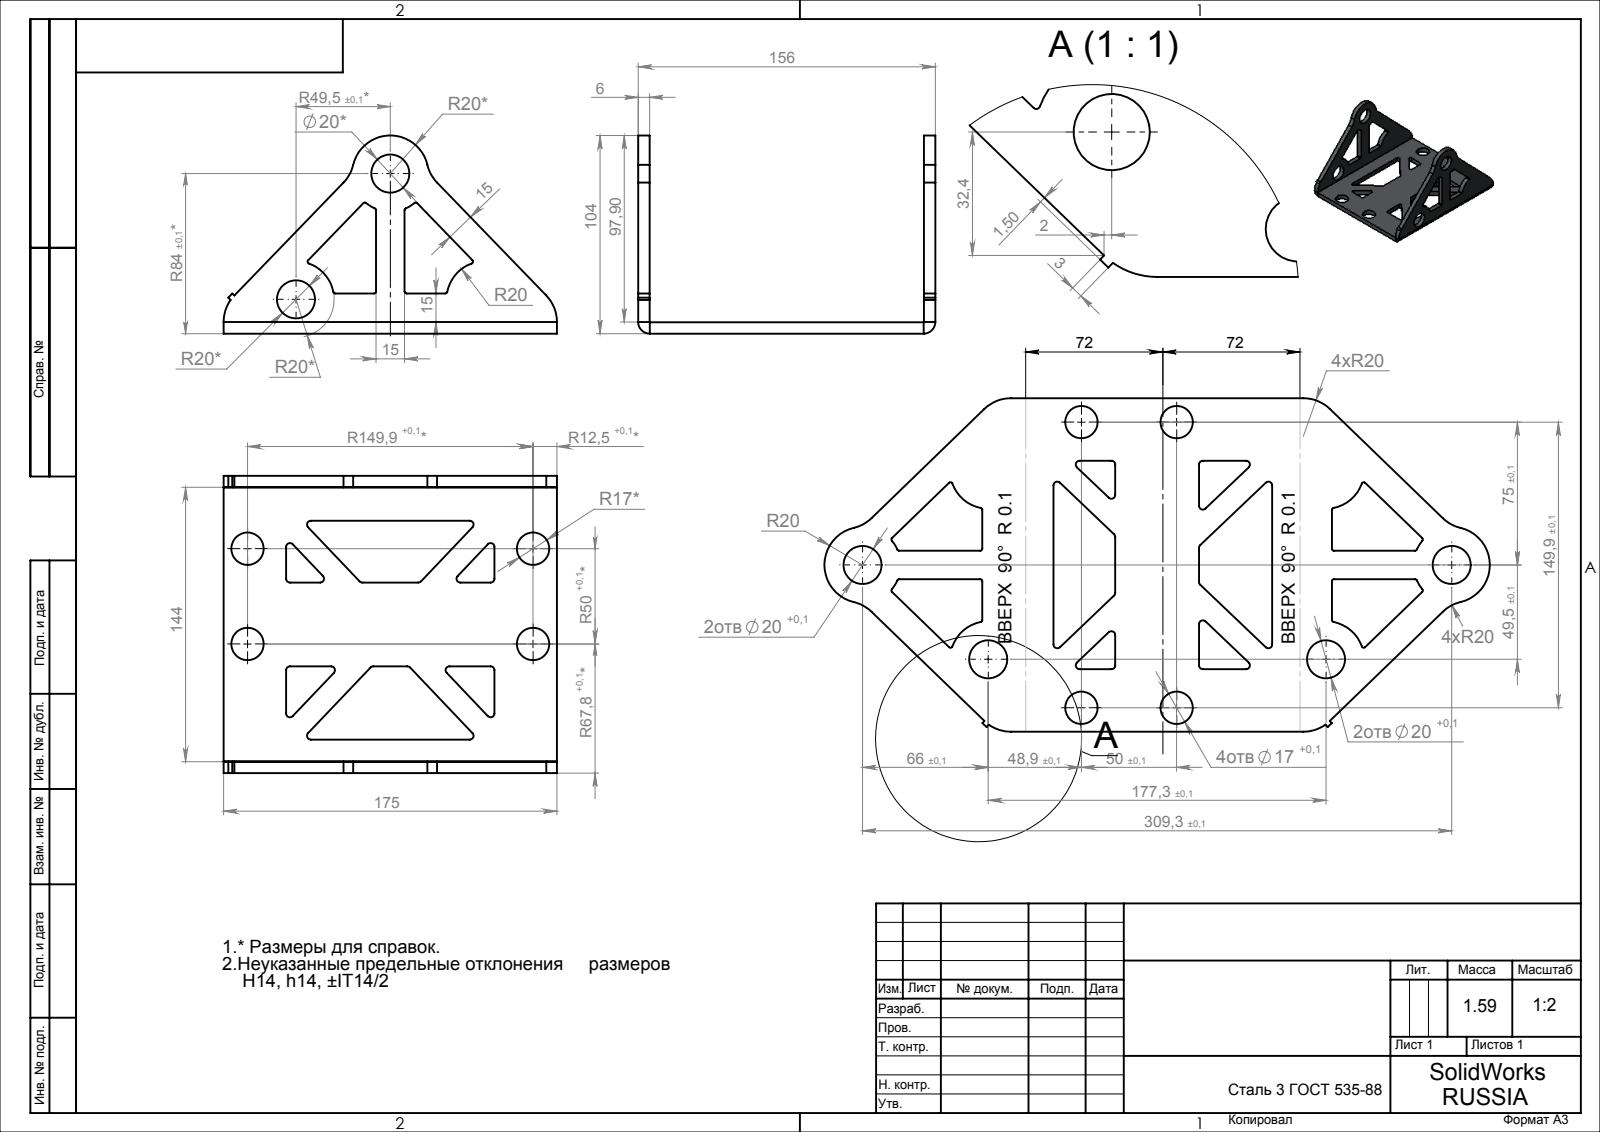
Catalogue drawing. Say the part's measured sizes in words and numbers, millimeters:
The part is named "Кронштейн". Its 3-D file was written by "SolidWorks 2018 (AUTOMOTIVE_DESIGN)". It is 1 solid with 118 faces: 40 planar, 70 cylindrical and 8 other. Overall it measures 305.35 by 195.6 by 3 millimeters. Its volume is 109 207 cubic millimeters and its surface area 82 517 square millimeters. Round holes: 6 of diameter 2.05, 4 of diameter 3, 4 of diameter 7. Partial cylindrical surfaces (rounded edges, fillets, slot ends): 34 of radius 3, 4 of radius 5. The main face-to-face distances are 3, 15, 20, 90.3, 105.3, 175.6, 85.3, 70.3, 195.6, 285.35. The hole center spacings are 44, 58.8, 39, 88, 96.25, 172.95, 185.02, 205.17.
